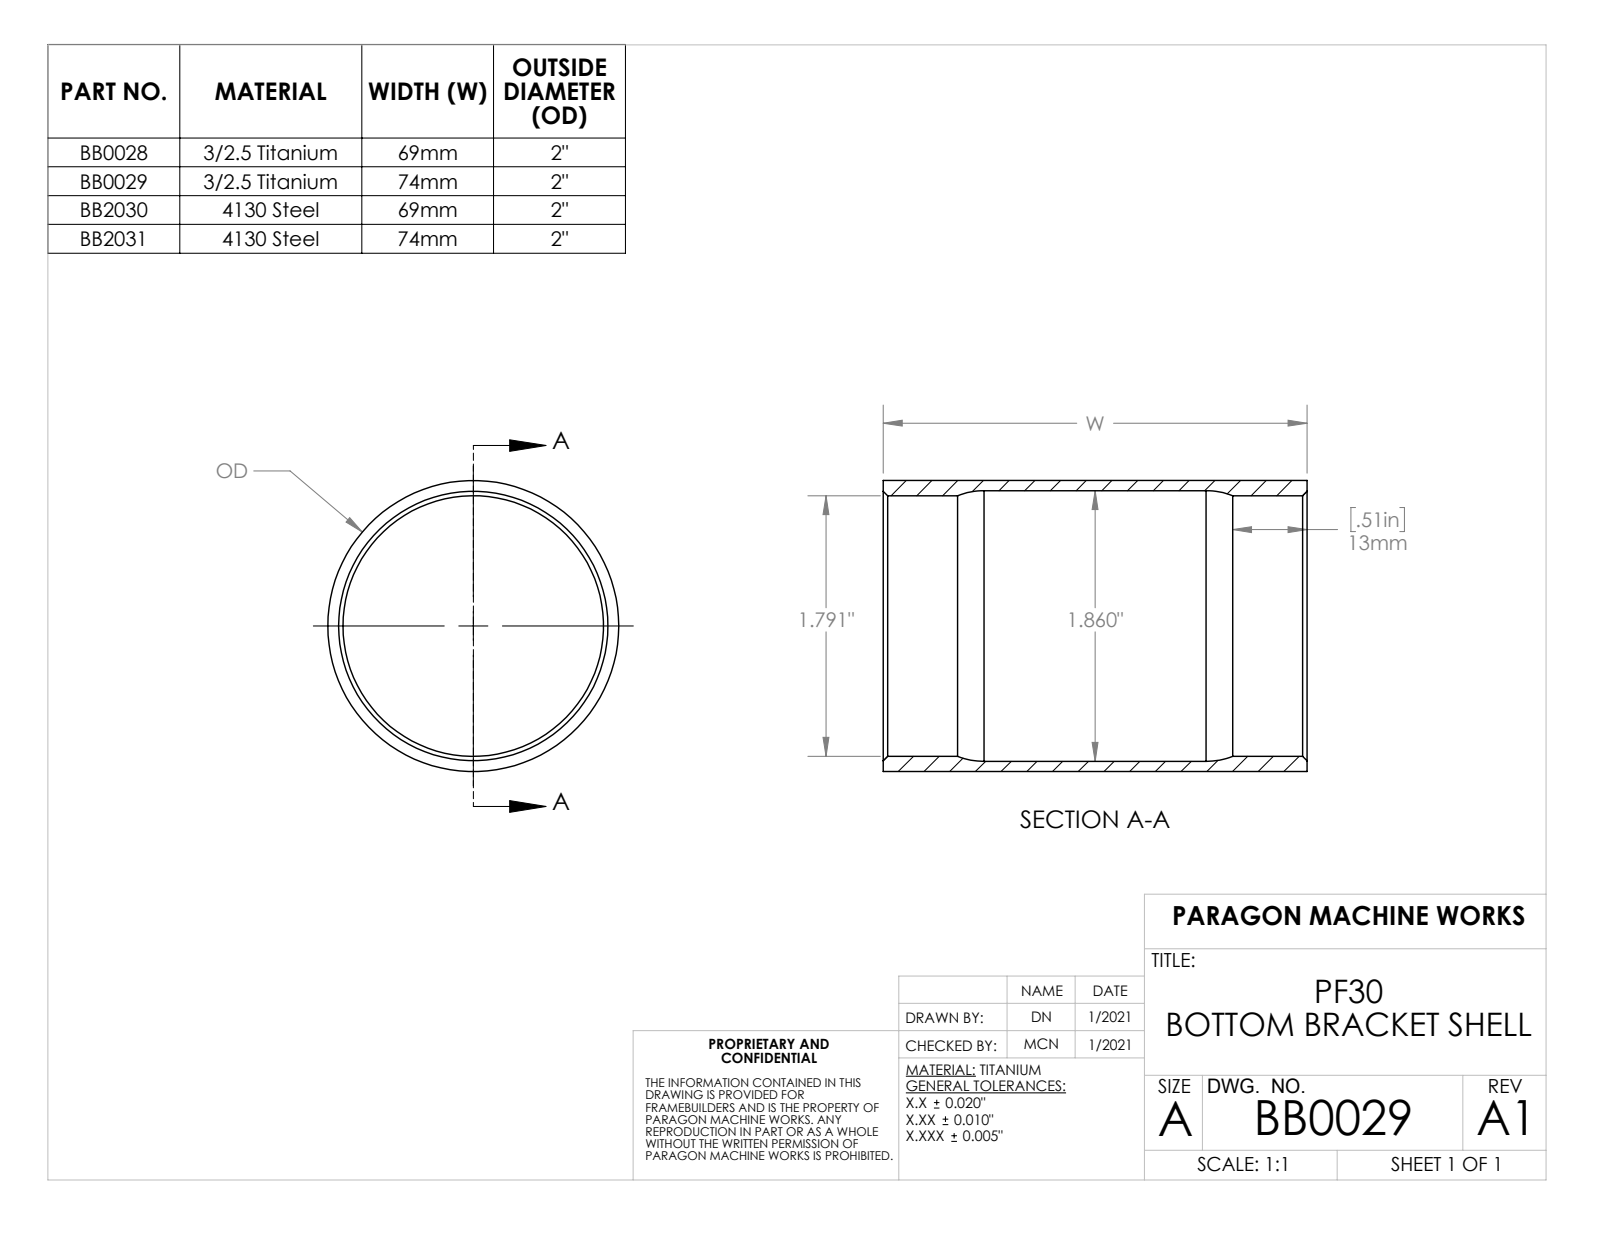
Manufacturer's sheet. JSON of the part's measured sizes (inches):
{"part_name": "BB0029", "step_written_by": "SolidWorks 2016 (AUTOMOTIVE_DESIGN)", "units": "inches", "bodies": {"solids": 1, "faces": 18, "planar": 2, "cylindrical": 8, "other": 8}, "overall_size": [2.913, 2, 2], "volume_in3": 1.457, "surface_area_in2": 36.18, "round_holes": [[1.791, 1], [1.86, 1]], "round_bosses_or_shafts": [[2, 1]], "face_to_face_distances": [2.913]}
